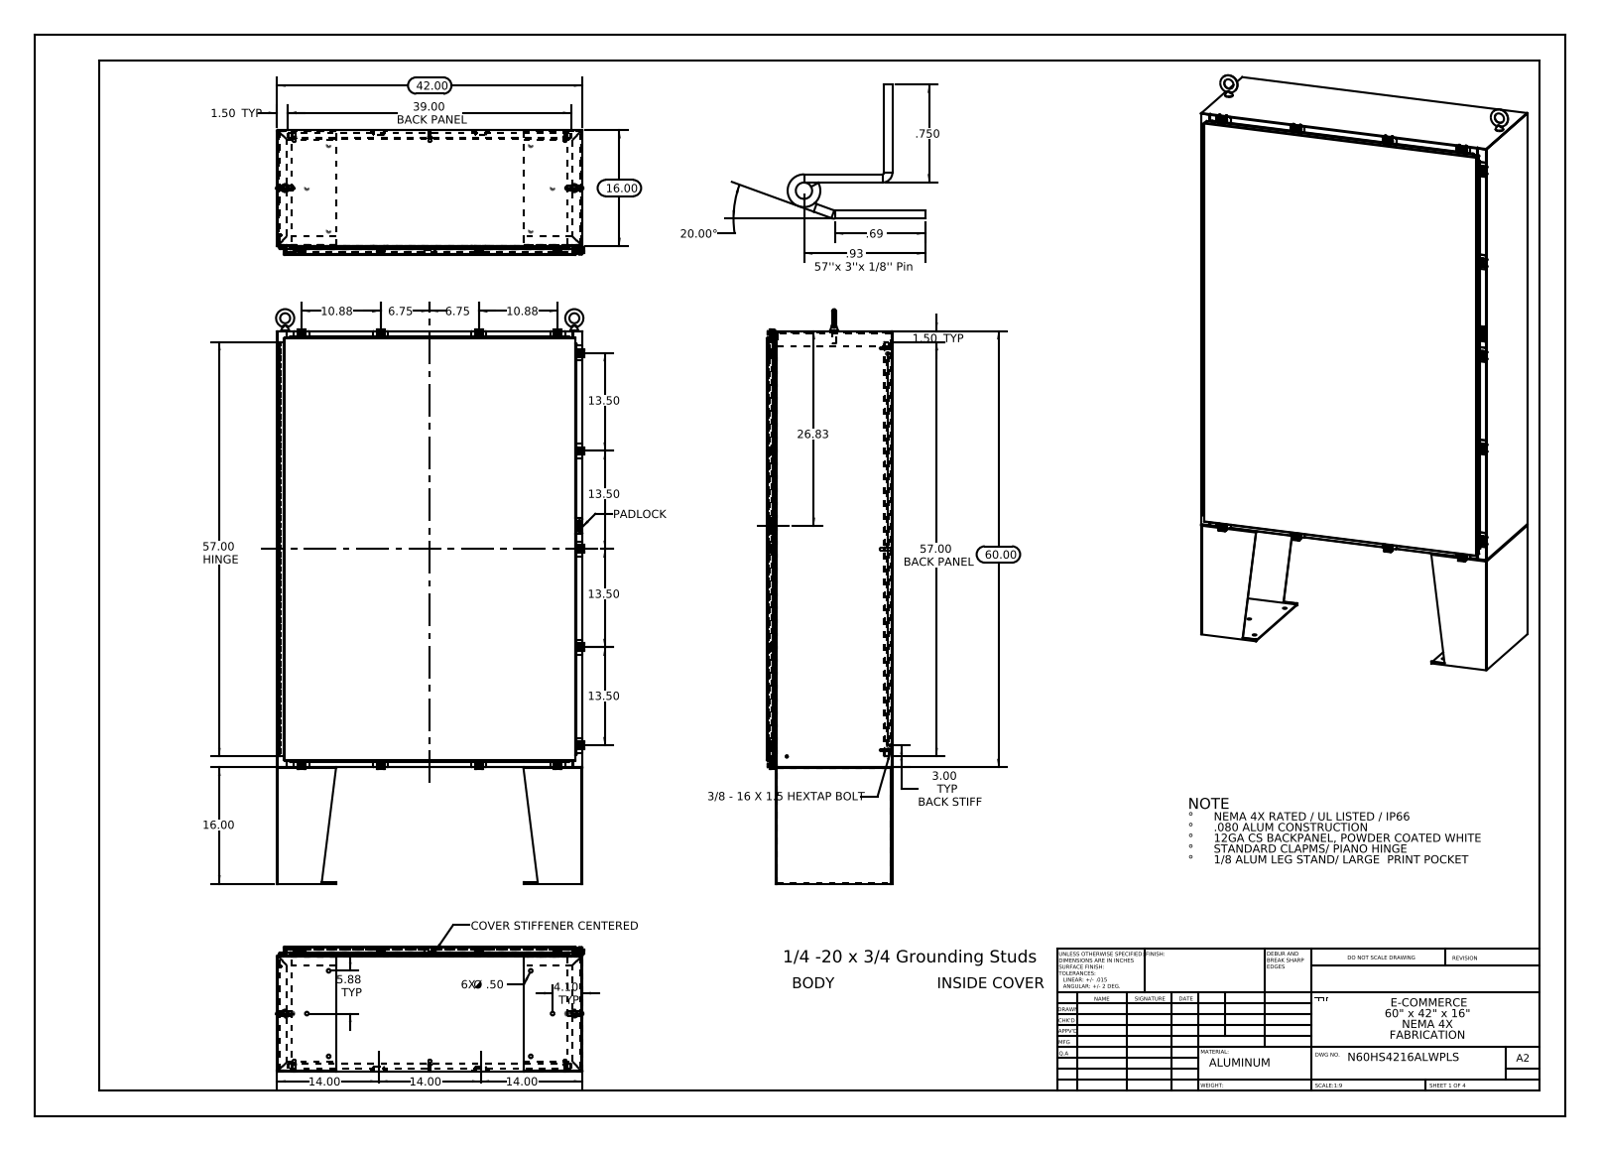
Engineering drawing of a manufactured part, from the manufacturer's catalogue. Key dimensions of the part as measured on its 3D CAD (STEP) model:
Part name (STEP PRODUCT): N60HS4216SSWPLS Clamp Top; N60HS4216SSWPLS Padlock Staple; N60HS4216SSWPLS Cover; N60HS4216SSWPLS Enclosure Stiffener (+8 more)
STEP written by: SolidWorks 2013 (CONFIG_CONTROL_DESIGN)
Units: inches
Bodies: 103 solids, 3908 faces (1992 planar, 1616 cylindrical, 300 other)
Overall size (bounding box): 79 × 42.346 × 17.201
Volume: 1 111 in³ · Surface area: 26 820 in²
Round holes (diameter × count): ⌀0.5 ×14, ⌀0.213 ×13, ⌀0.26 ×13, ⌀0.25 ×8, ⌀0.75 ×4, ⌀0.125 ×2, ⌀0.125 ×1
Round bosses / shafts (diameter × count): ⌀0.25 ×14, ⌀0.5 ×13, ⌀0.399 ×13, ⌀0.625 ×10, ⌀0.375 ×8, ⌀0.33 ×8, ⌀0.157 ×8, ⌀0.14 ×8
Partial cylindrical surfaces — rounded edges, fillets, slot ends (radius × count): R0.06 ×58, R0.013 ×39, R0.088 ×33, R0.12 ×26, R0.141 ×26, R0.05 ×23, R0.145 ×22, R0.08 ×18
Main face-to-face distances: 0.075, 17.126, 0.104, 17.051, 1.075, 17.201, 1, 16.126, 16.051, 1.179
Hole centre spacings: 13.5, 2.225, 7.069, 8.393, 27.625, 29.743, 31.348, 32.01
